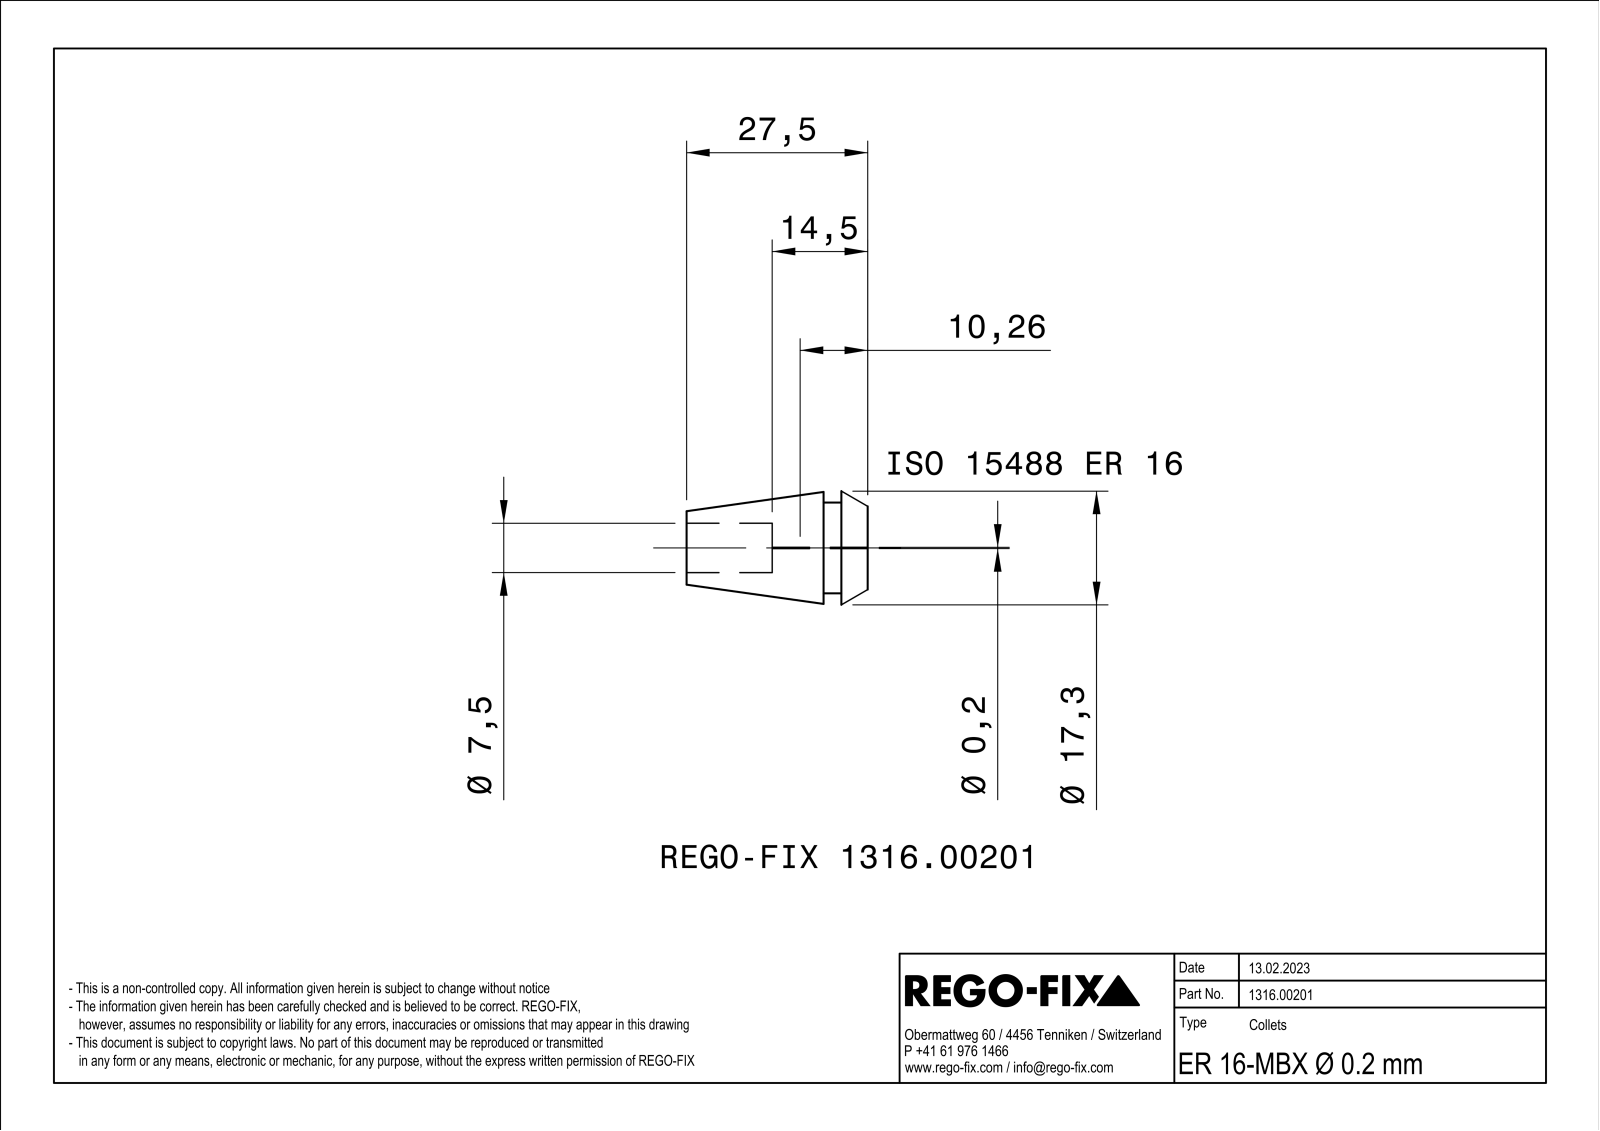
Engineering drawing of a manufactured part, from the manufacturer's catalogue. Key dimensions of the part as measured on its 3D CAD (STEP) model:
Part name (STEP PRODUCT): NOCUT
STEP written by: SIEMENS PLM Software Solid Edge ST10 (AUTOMOTIVE_DESIGN)
Units: millimetres
Bodies: 1 solid, 109 faces (36 planar, 27 cylindrical, 46 other)
Overall size (bounding box): 27.5 × 16.91 × 16.9
Volume: 3 347 mm³ · Surface area: 3 341 mm²
Round holes (diameter × count): ⌀2 ×3, ⌀7.5 ×1
Round bosses / shafts (diameter × count): ⌀13.8 ×1
Partial cylindrical surfaces — rounded edges, fillets, slot ends (radius × count): R25 ×3, R0.1 ×1
Main face-to-face distances: 0.34, 0.46, 0.8, 6.7, 4, 2.7, 27.5, 23.5, 20.8, 14.5
Hole centre spacings: 2.1, 3.64
